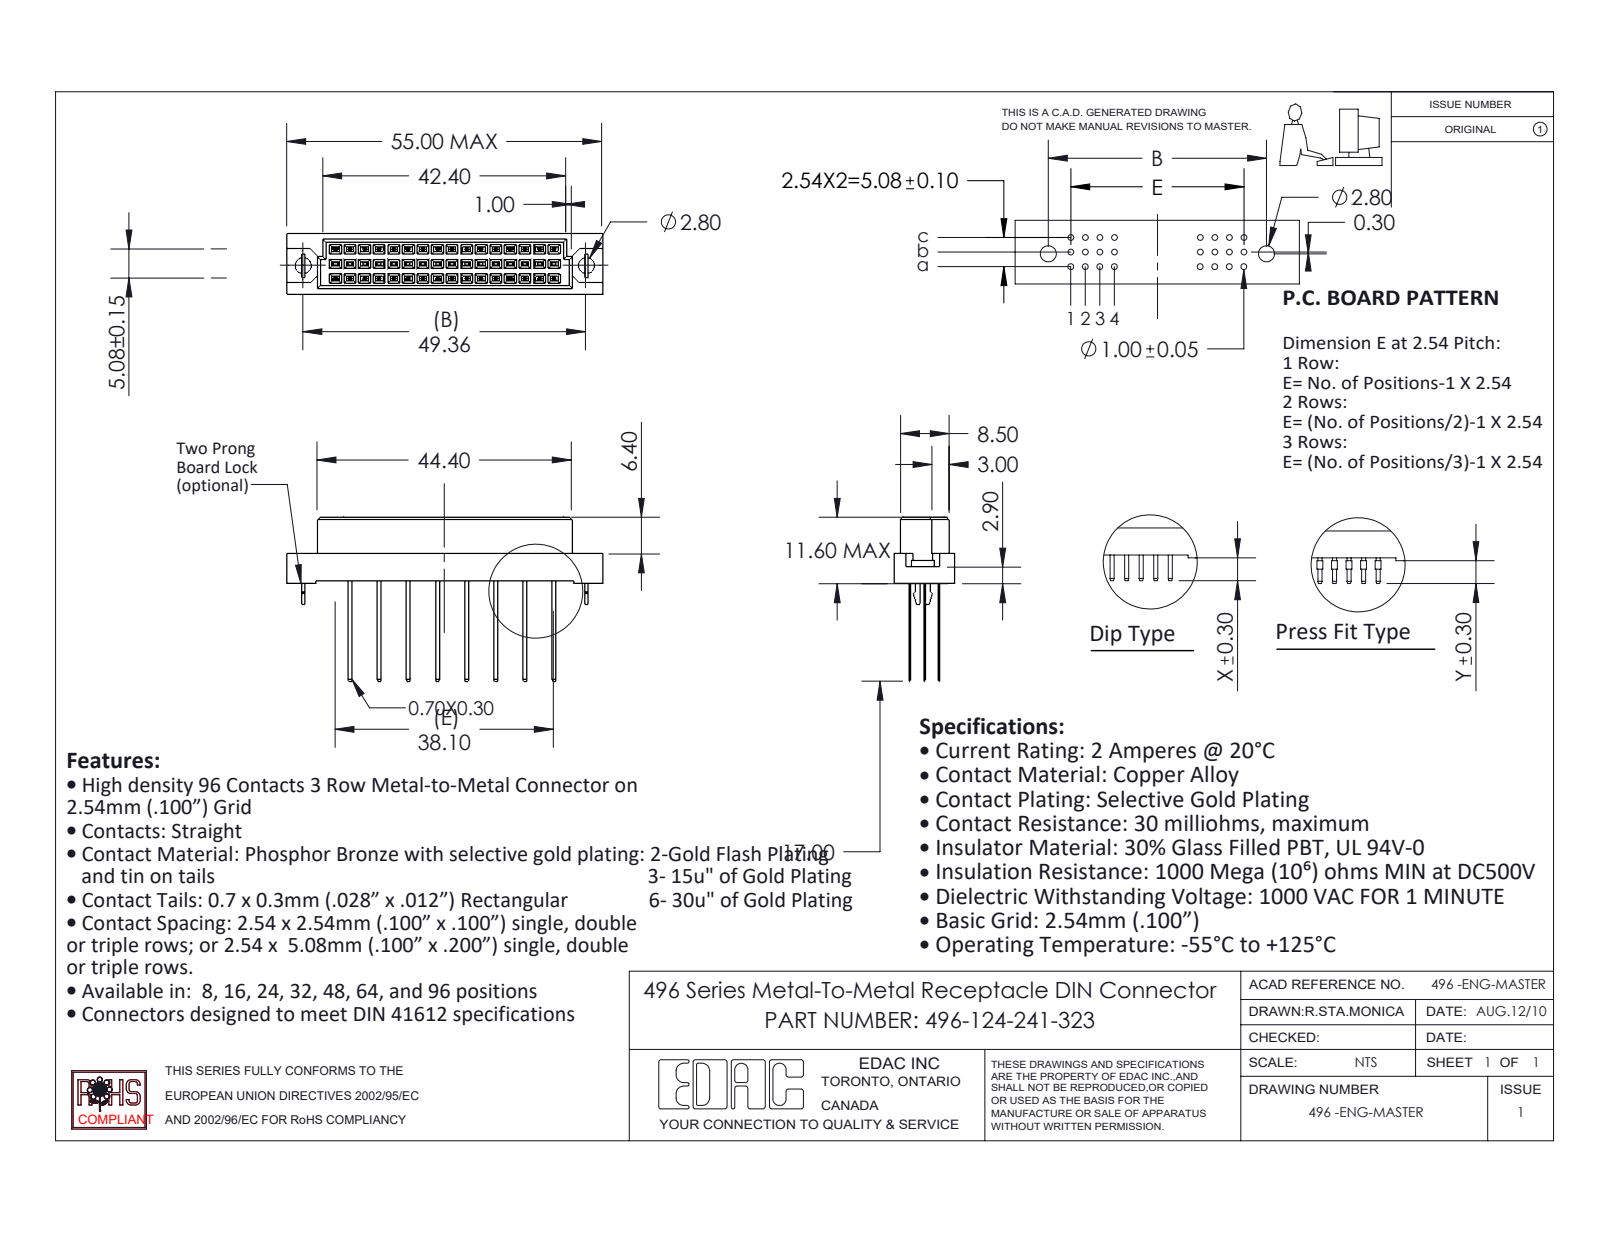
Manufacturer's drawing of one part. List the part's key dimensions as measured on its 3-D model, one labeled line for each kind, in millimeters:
Part name (STEP PRODUCT): 496-290_41; 496 Bore-lock; 496-124-241-323; 496 Part_48
STEP written by: SolidWorks 2020 (CONFIG_CONTROL_DESIGN)
Units: millimetres
Bodies: 27 solids, 942 faces (936 planar, 6 cylindrical, 0 other)
Overall size (bounding box): 55 × 28.6 × 10.6
Volume: 4 719 mm³ · Surface area: 5 356 mm²
Round holes (diameter × count): ⌀2.8 ×2
Partial cylindrical surfaces — rounded edges, fillets, slot ends (radius × count): R0.53 ×1
Main face-to-face distances: 2.54, 5.08, 1.05, 9.55, 0.56, 0.55, 0.81, 2.84, 1.56, 1.86
Hole centre spacings: 49.36
